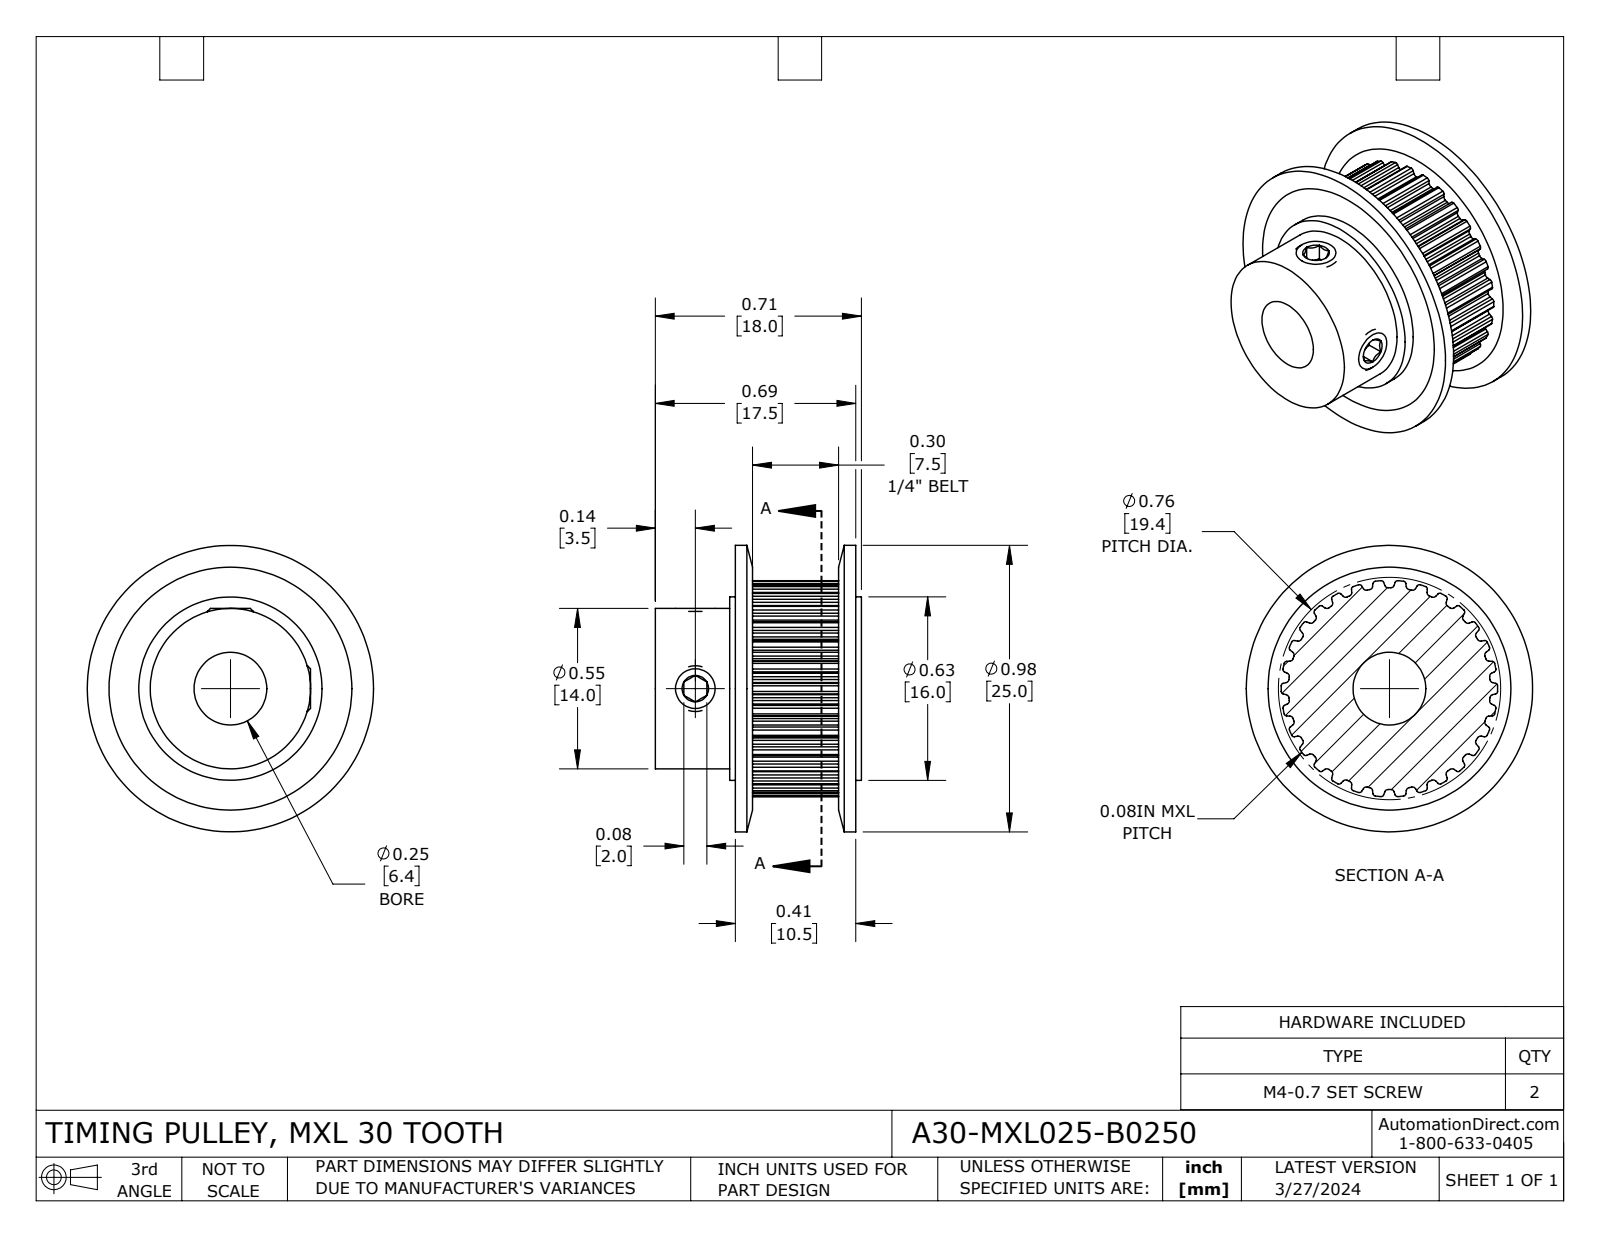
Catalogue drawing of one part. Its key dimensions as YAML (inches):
part_name: "A30-MXL025-B0250"
step_written_by: "SolidWorks 2021 (CONFIG_CONTROL_DESIGN)"
units: inches
bodies: {solids: 5, faces: 348, planar: 85, cylindrical: 229, other: 34}
overall_size: [0.984, 0.984, 0.709]
volume: 0.231
surface_area: 5.453
round_holes:
  - {diameter: 0.13, count: 2}
  - {diameter: 0.25, count: 1}
  - {diameter: 0.63, count: 1}
round_bosses_or_shafts:
  - {diameter: 0.157, count: 2}
  - {diameter: 0.984, count: 1}
  - {diameter: 0.551, count: 1}
partial_cylinders:
  - {radius: 0.009, count: 60}
  - {radius: 0.012, count: 60}
  - {radius: 0.347, count: 1}
  - {radius: 0.372, count: 1}
face_to_face_distances: [0.039, 0.335, 0.374, 0.295, 0.079, 0.413, 0.709, 0.669, 0.63, 0.453]
